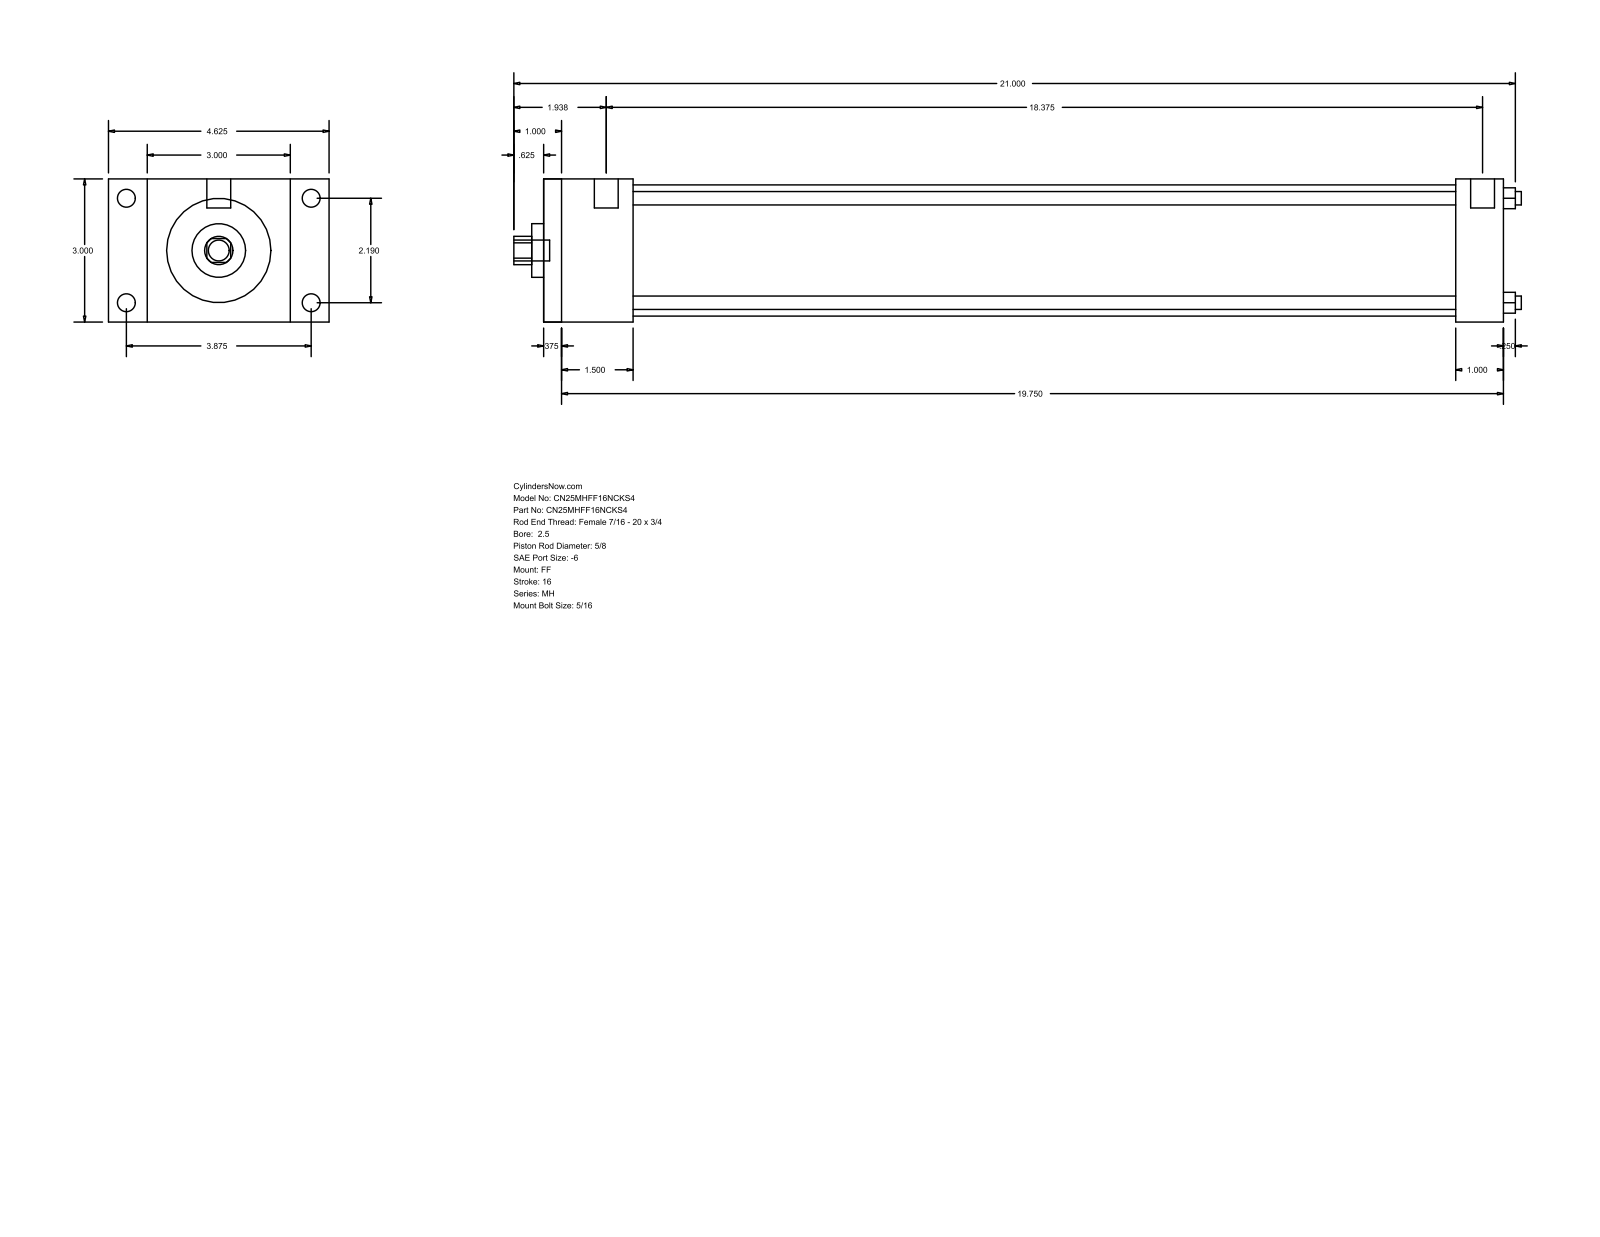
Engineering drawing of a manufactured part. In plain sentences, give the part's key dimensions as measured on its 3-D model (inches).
The part is named "MH_FF__0250_0.625". Its 3-D file was written by "GSSL Pune (CONFIG_CONTROL_DESIGN)". It is 0 solids with 92 faces: 64 planar, 28 cylindrical and 0 other. Overall it measures 21.125 by 4.625 by 3 inches. Round holes: 4 of diameter 0.281, 1 of diameter 0.625, 1 of diameter 1.125, 1 of diameter 2.75. Round bosses or shafts: 4 of diameter 0.375, 4 of diameter 0.219, 2 of diameter 0.5, 1 of diameter 0.437. Partial cylindrical surfaces (rounded edges, fillets, slot ends): 1 of radius 0.297. The main face-to-face distances are 3, 20.125, 0.375, 19.75, 1, 1.875, 19.125, 1.5, 18.75, 17.25. The hole center spacings are 1.548, 2.19, 3.097.
